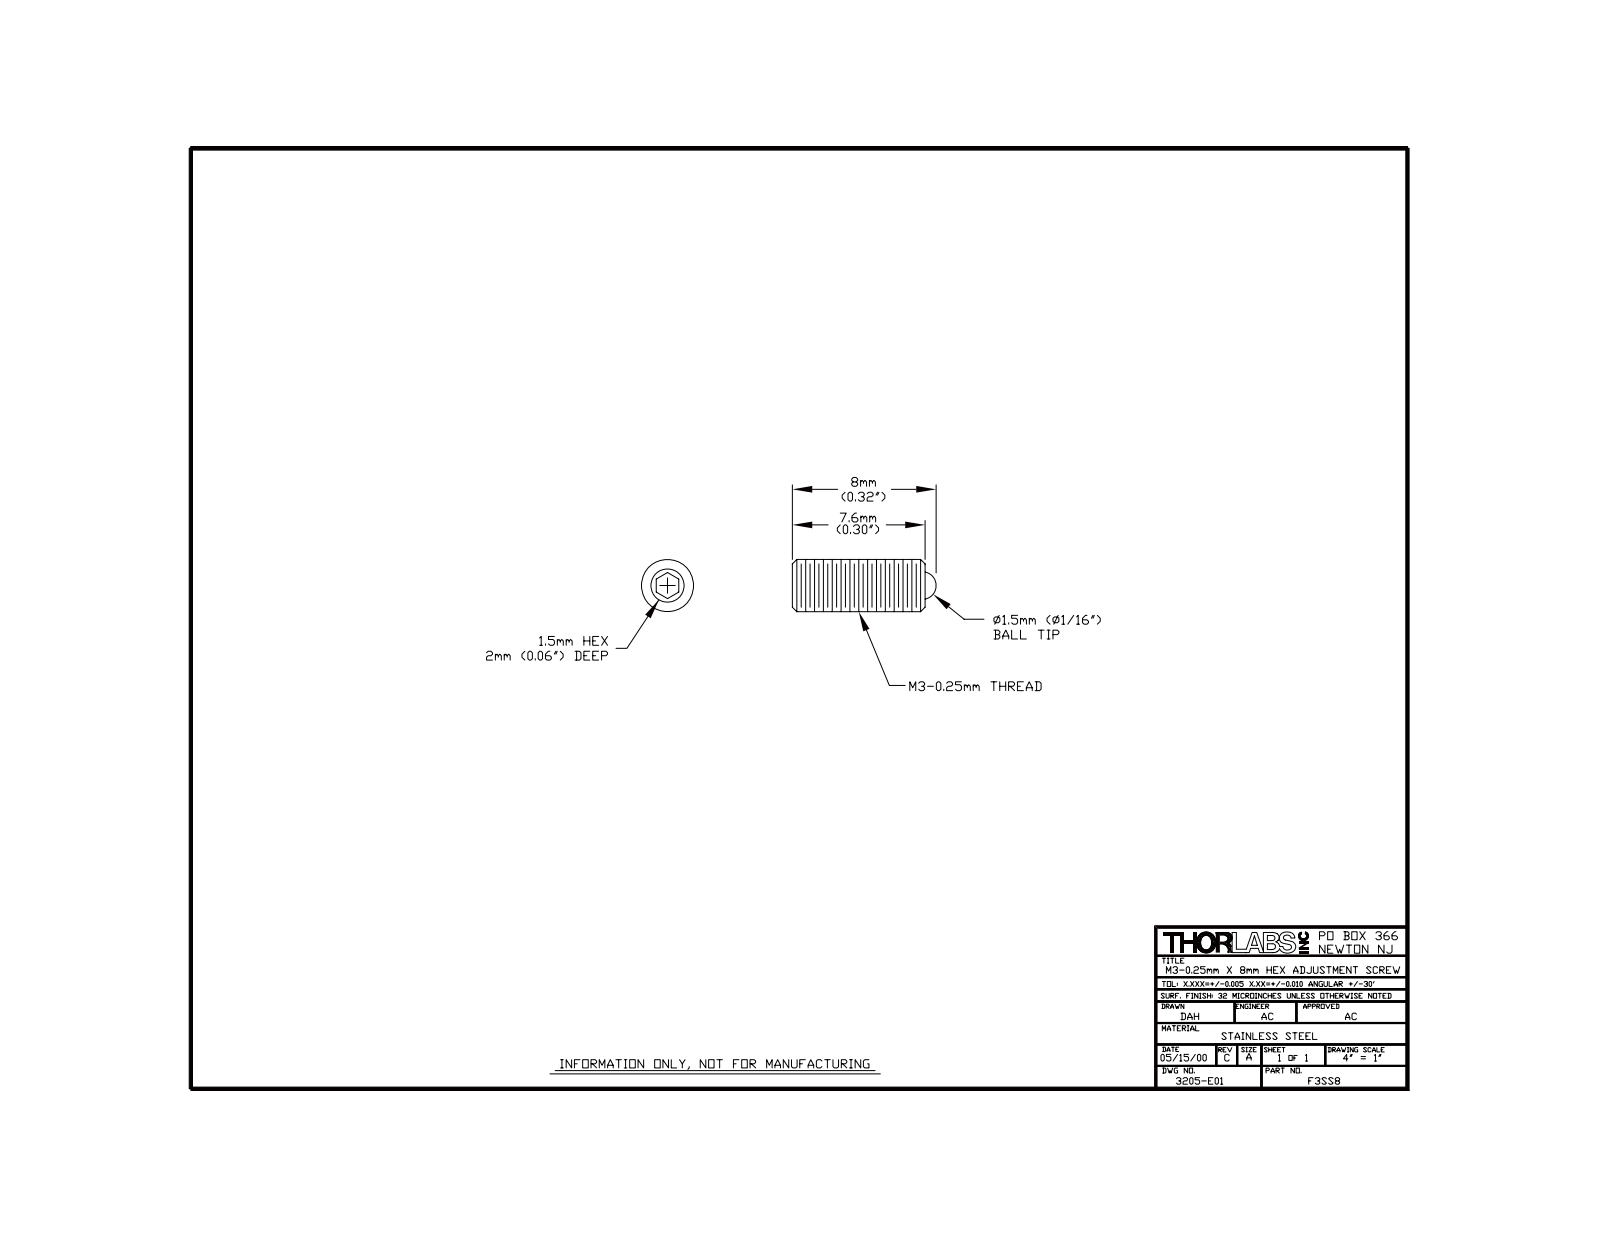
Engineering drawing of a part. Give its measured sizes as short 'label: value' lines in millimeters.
name: 3205-E0W
written by: SolidWorks 2011 (AUTOMOTIVE_DESIGN)
unit: mm
bodies: 2 solids, 23 faces (9 planar, 4 cylindrical, 10 other)
size: 8.3 × 3 × 3
volume: 50 mm³; area: 100 mm²
holes: 1× ⌀1.6
bosses: 1× ⌀3
face distances: 7.6, 1.3, 1.5, 6.1, 1.3
